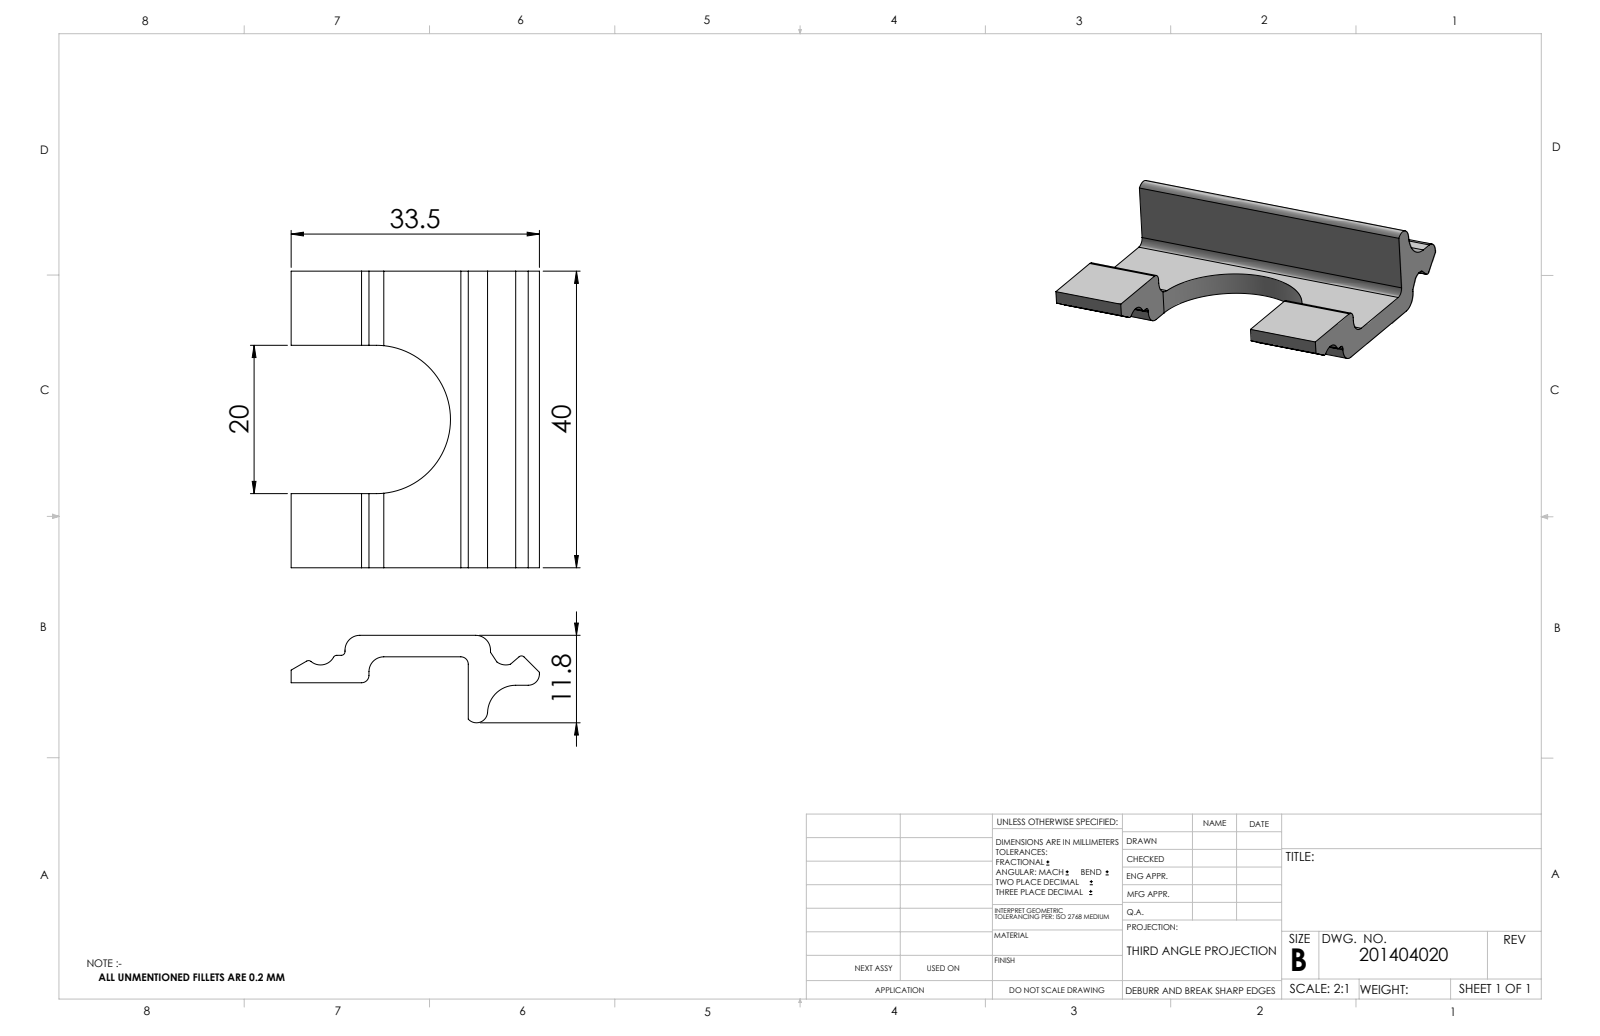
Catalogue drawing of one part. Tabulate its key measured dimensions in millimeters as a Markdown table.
| quantity | value |
| --- | --- |
| part name | 201404020_c_1 |
| STEP written by | SolidWorks 2020 (AUTOMOTIVE_DESIGN) |
| units | millimeters |
| bodies | 1 solid, 47 faces (25 planar, 22 cylindrical, 0 other) |
| overall size | 40 × 33.5 × 11.8 |
| volume | 4 075 mm³ |
| surface area | 3 106 mm² |
| partial cylindrical surfaces (radius × count) | 2 × 5, 0.5 × 4, 1 × 2, 1.5 × 1, 1.51 × 1, 3.8 × 1, 10 × 1 |
| main face-to-face distances | 2.9, 6.4, 3.5, 40, 10, 30, 6.74, 3.84, 0.34, 20 |
